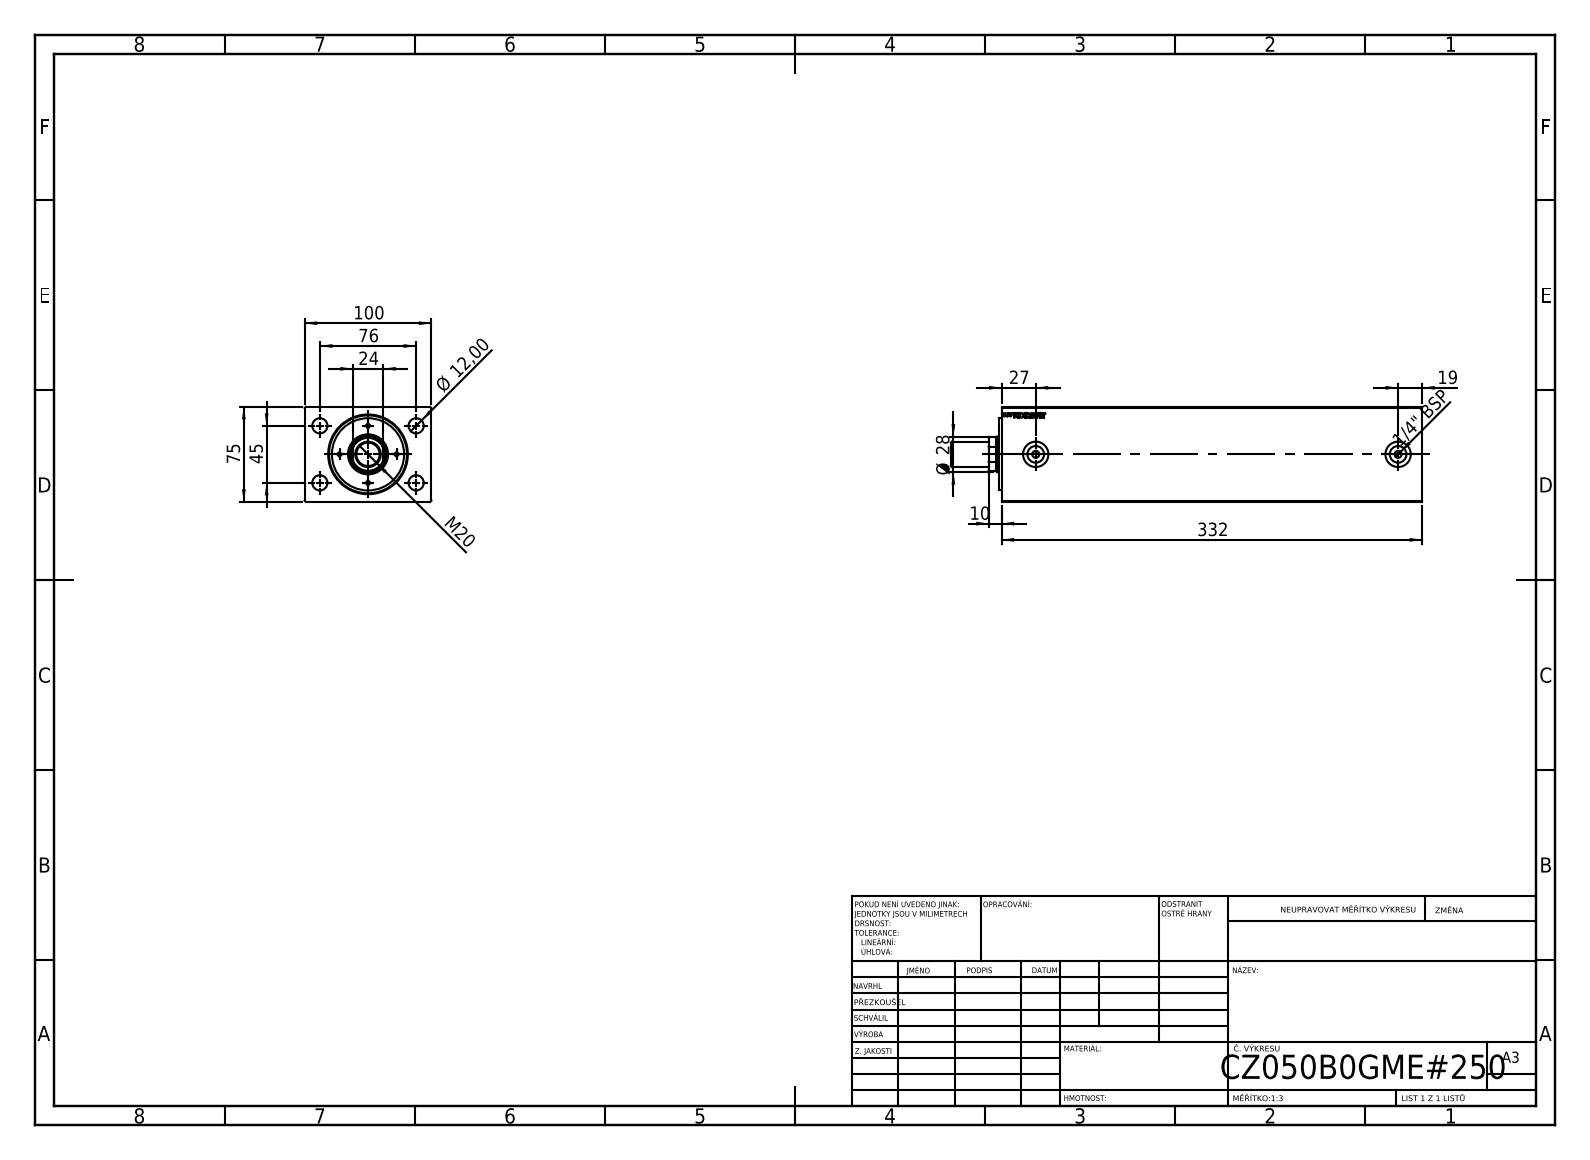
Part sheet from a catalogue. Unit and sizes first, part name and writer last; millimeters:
Units: millimetres
Overall size (bounding box): 372 × 100 × 75
Round holes (diameter × count): ⌀3 ×4, ⌀12 ×4, ⌀5.5 ×2, ⌀13.16 ×2, ⌀20 ×2, ⌀18.5 ×1, ⌀28 ×1, ⌀29 ×1, ⌀36 ×1, ⌀50 ×1, ⌀61.5 ×1
Round bosses / shafts (diameter × count): ⌀57 ×1, ⌀20 ×1
Partial cylindrical surfaces — rounded edges, fillets, slot ends (radius × count): R13.5 ×1
Main face-to-face distances: 75, 100, 332, 314.2, 17.8, 10, 8.2, 1.8, 306, 323.8
Hole centre spacings: 22.5, 27.32, 31.82, 38, 44.16, 45, 58.9, 64.55
Volume: 2 131 000 mm³ · Surface area: 236 825 mm²
Bodies: 4 solids, 880 faces (402 planar, 60 cylindrical, 418 other)
Part name (STEP PRODUCT): V500CZ_B_VC; V500CZ; V500CZ_SMALL_MALE_METRIC
STEP written by: SolidWorks 2019 (CONFIG_CONTROL_DESIGN)
